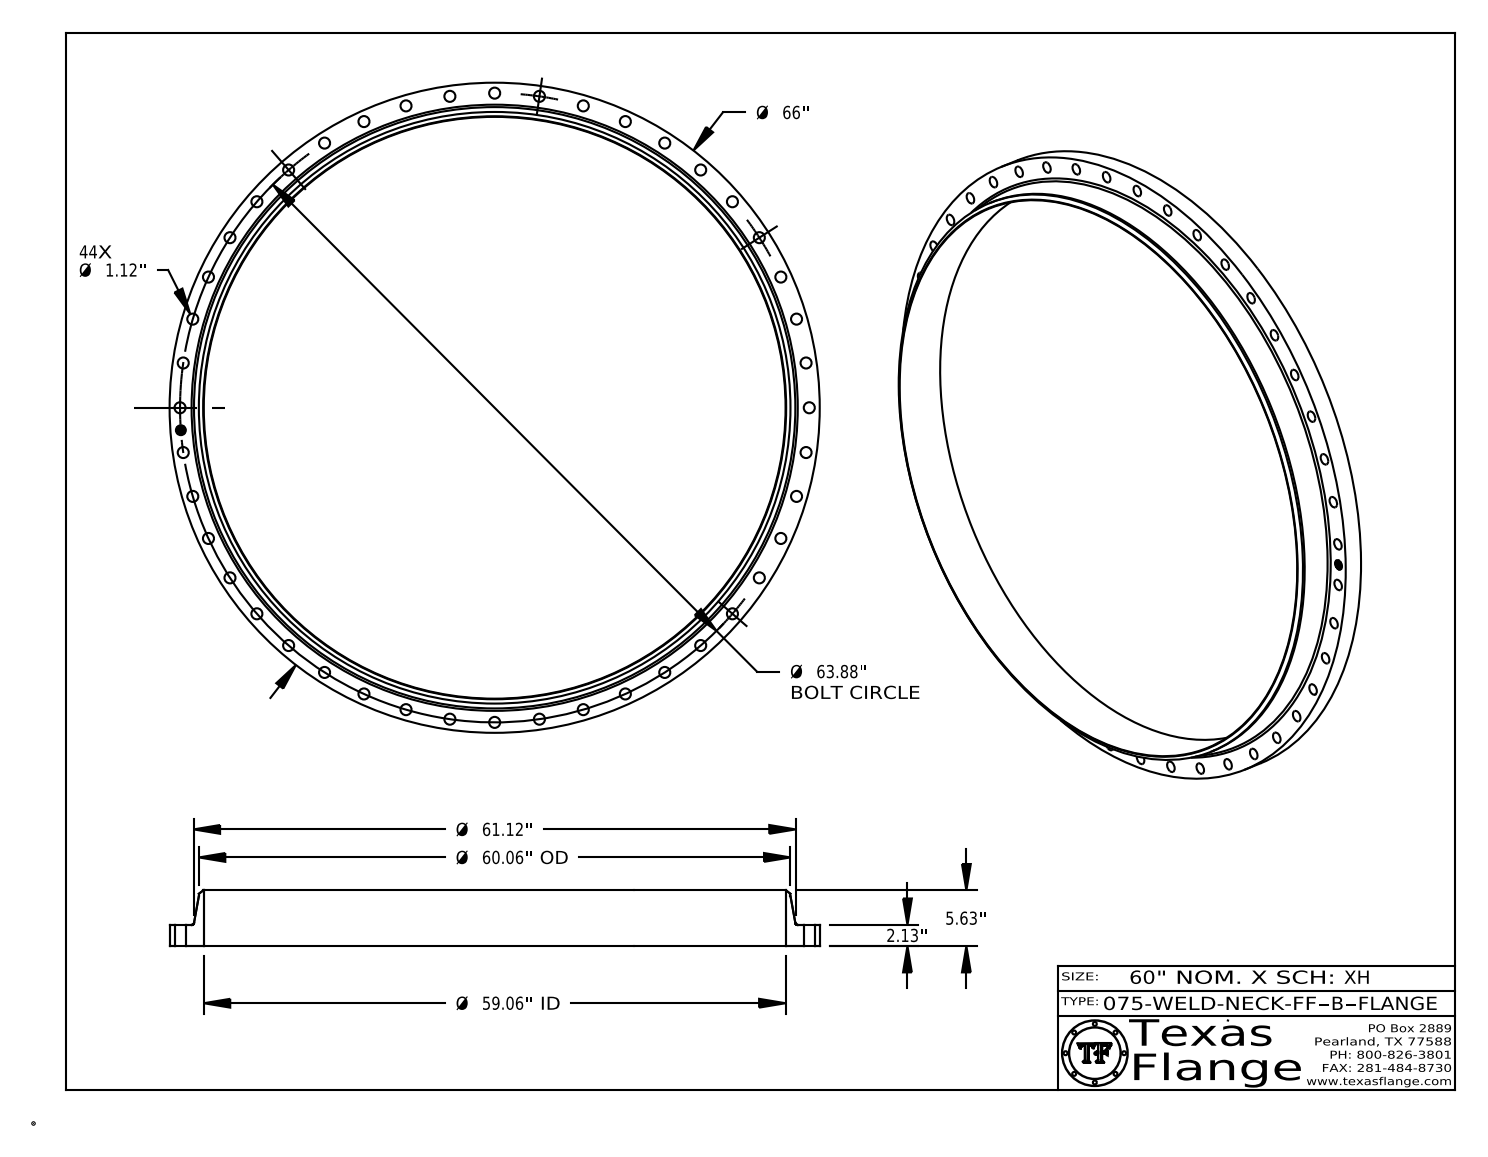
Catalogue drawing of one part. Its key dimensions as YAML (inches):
part_name: "075-WELD-NECK-FF, Series B"
step_written_by: "CATIA V5 STEP AP214 (AUTOMOTIVE_DESIGN)"
units: inches
bodies: {solids: 1, faces: 488, planar: 368, cylindrical: 114, other: 6}
overall_size: [66, 66, 5.63]
volume: 1822
surface_area: 3611
round_holes:
  - {diameter: 1.12, count: 44}
  - {diameter: 1, count: 1}
  - {diameter: 59.06, count: 1}
round_bosses_or_shafts:
  - {diameter: 0.061, count: 8}
  - {diameter: 66, count: 1}
  - {diameter: 60.06, count: 1}
  - {diameter: 0.788, count: 1}
face_to_face_distances: [2.13, 5.63, 3.5, 2.115, 0.015, 3.515, 0.298, 0.293, 0.054, 0.193]
hole_center_spacings: [9.091, 13.579, 31.94, 63.717, 4.557, 63.23, 26.537, 59.852]
